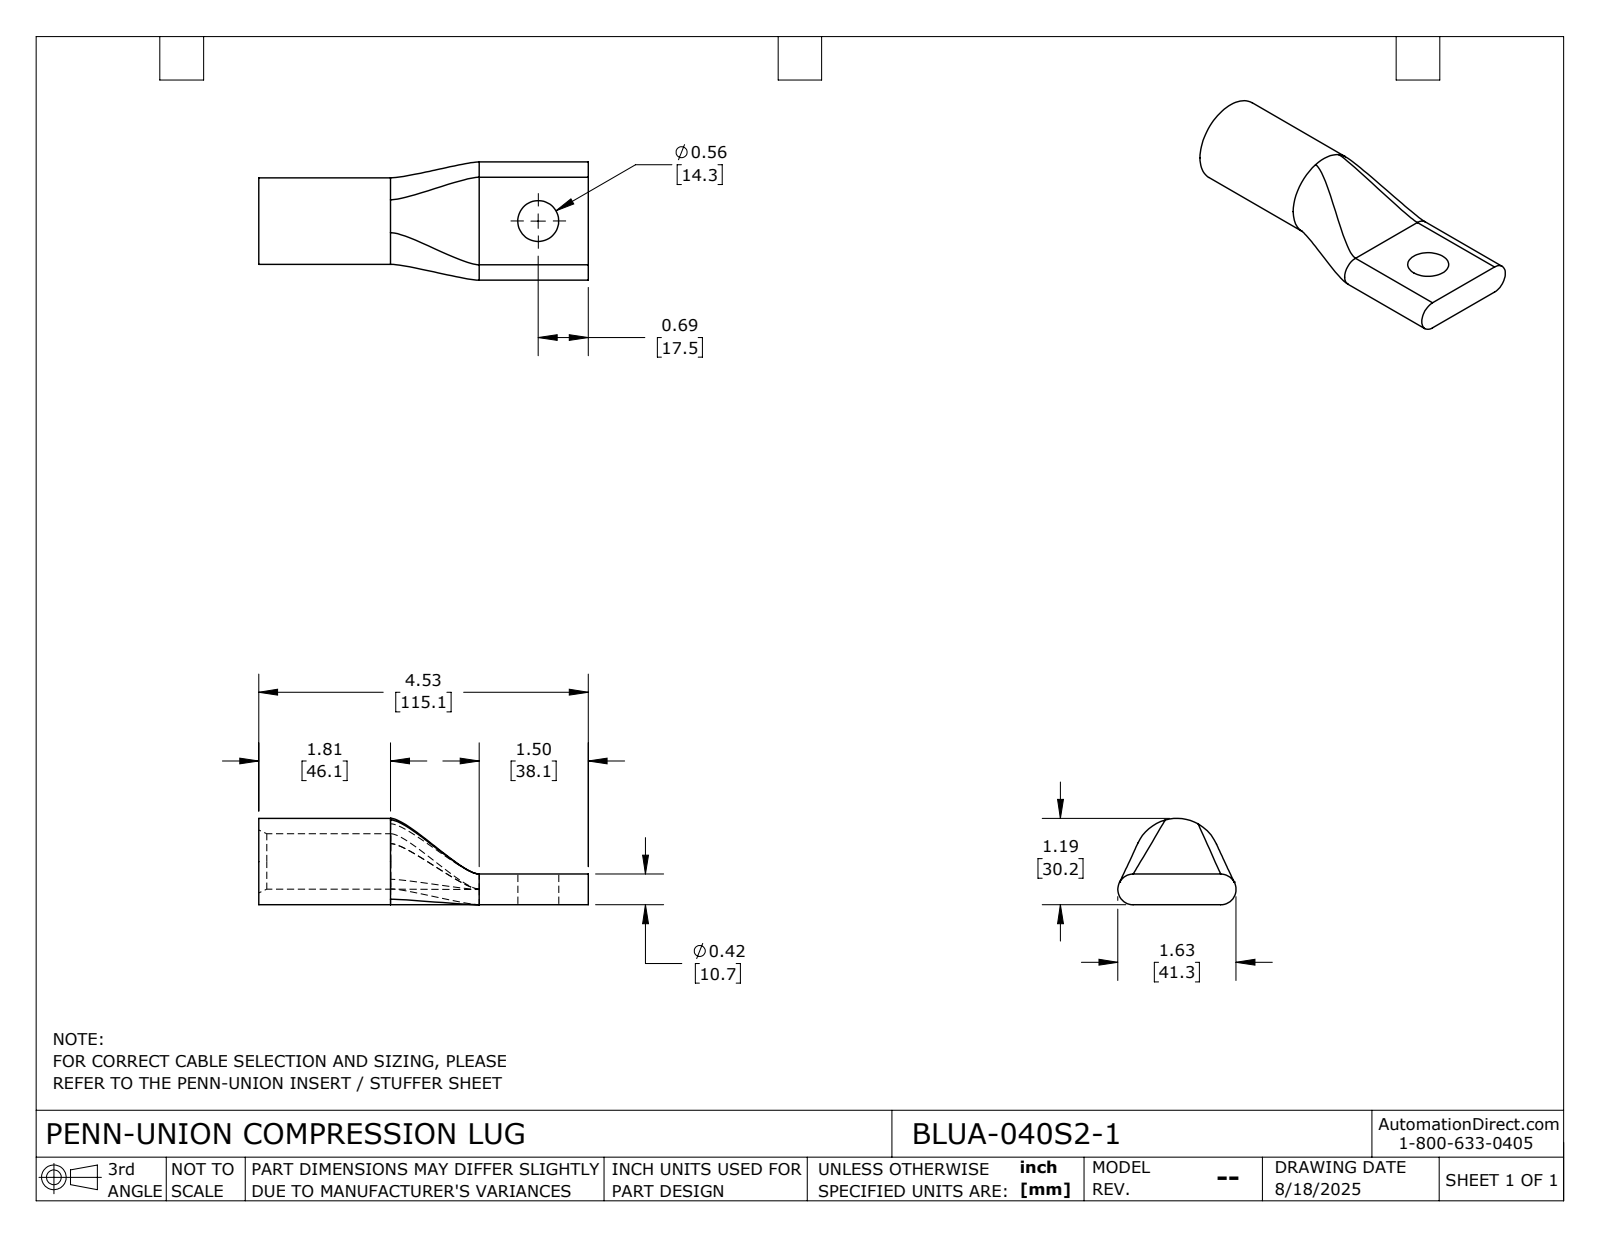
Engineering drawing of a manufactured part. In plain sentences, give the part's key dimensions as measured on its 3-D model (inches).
The part is named "BLUA-040S2-1". Its 3-D file was written by "SolidWorks 2024 (CONFIG_CONTROL_DESIGN)". It is 1 solid with 24 faces: 5 planar, 9 cylindrical and 10 other. Overall it measures 4.531 by 1.625 by 1.188 inches. Its volume is 2.828 cubic inches and its surface area 26.02 square inches. Round holes: 1 of diameter 0.563, 1 of diameter 0.762. Round bosses or shafts: 1 of diameter 1.188. Partial cylindrical surfaces (rounded edges, fillets, slot ends): 2 of radius 0.211. The main face-to-face distances are 0.422, 4.531, 3.031, 1.5.
